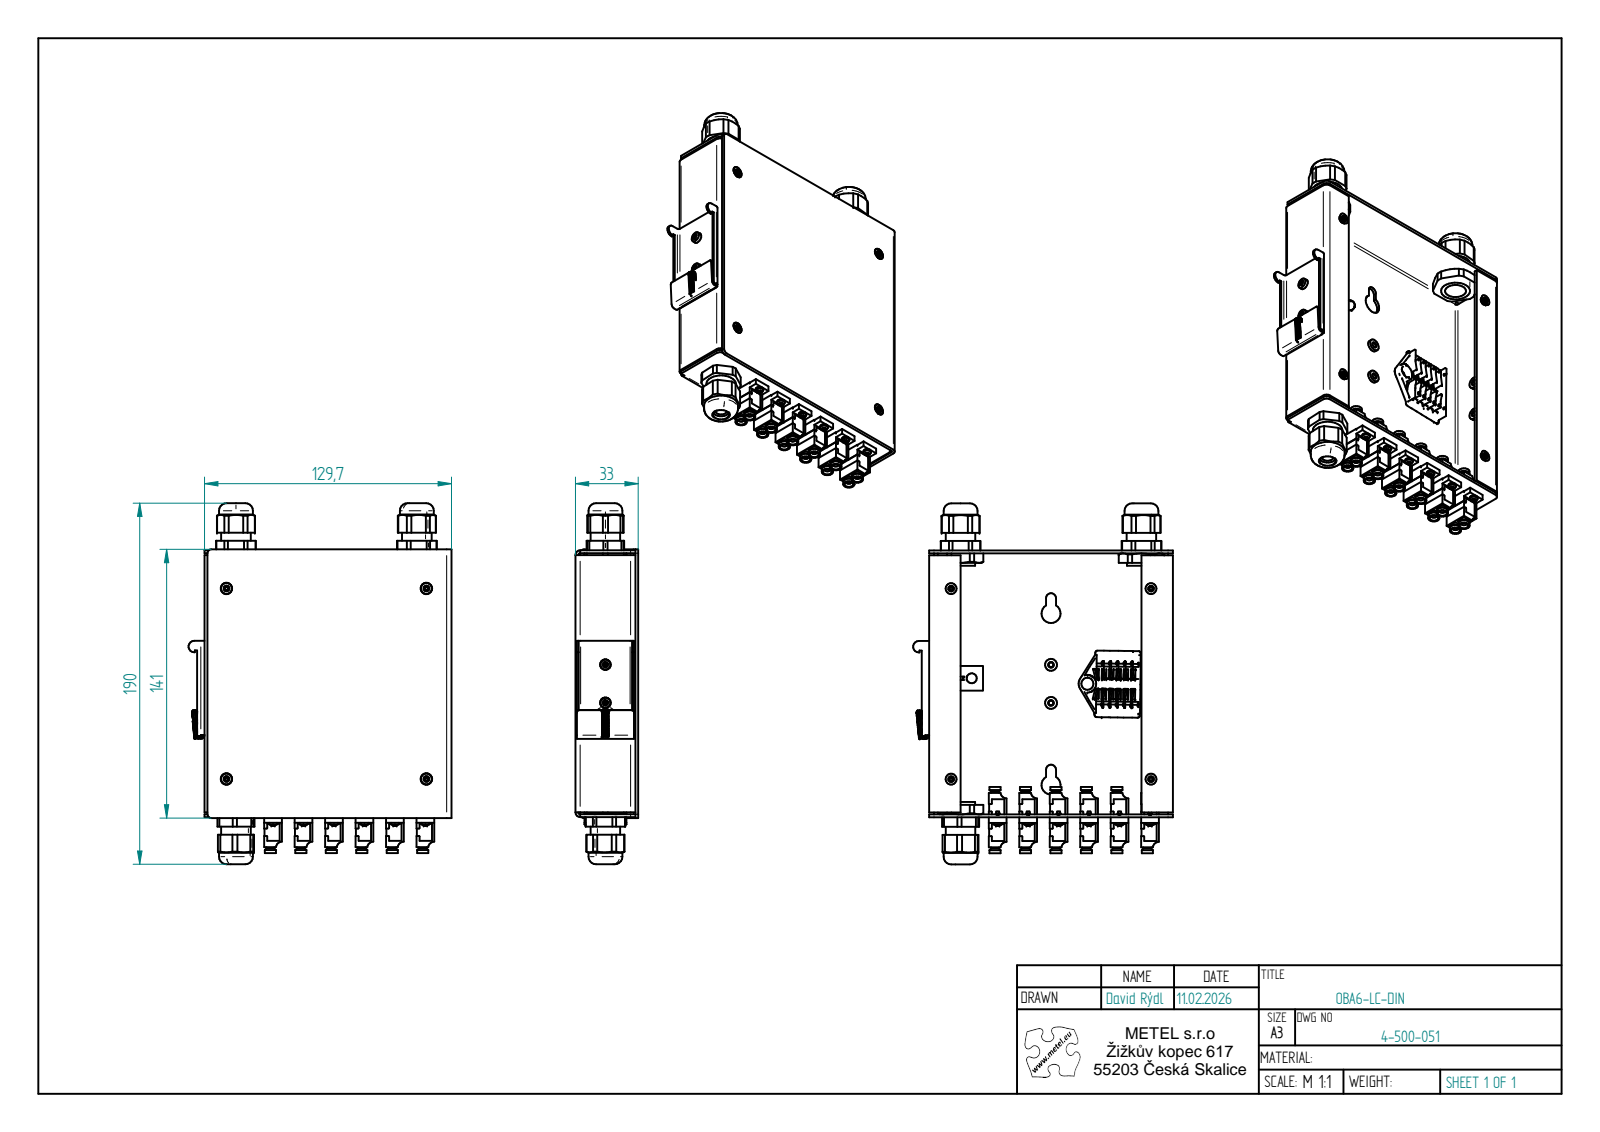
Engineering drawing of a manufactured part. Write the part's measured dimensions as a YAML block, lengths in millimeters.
part_name: "OBA6-LC-DIN; OBA6-DIN_Spodni dil_sestava 2; OBA6-DIN_Spodni dil 2; 19751v-s-m3-2_zi (+8 more)"
step_written_by: "Solid Edge (AUTOMOTIVE_DESIGN)"
units: millimeters
bodies: {solids: 68, faces: 57264, planar: 55759, cylindrical: 847, other: 658}
overall_size: [189.55, 138.11, 33]
volume: 122221
surface_area: 179238
round_holes:
  - {diameter: 3, count: 16}
  - {diameter: 1.8, count: 12}
  - {diameter: 2.03, count: 12}
  - {diameter: 2.49, count: 12}
  - {diameter: 2.5, count: 12}
  - {diameter: 2.46, count: 8}
  - {diameter: 4, count: 4}
  - {diameter: 3.5, count: 2}
  - {diameter: 6, count: 2}
  - {diameter: 8.5, count: 2}
  - {diameter: 9, count: 2}
  - {diameter: 10, count: 2}
round_bosses_or_shafts:
  - {diameter: 5.85, count: 12}
  - {diameter: 4.2, count: 12}
  - {diameter: 4, count: 12}
  - {diameter: 2.74, count: 12}
  - {diameter: 1.5, count: 12}
  - {diameter: 6.3, count: 8}
  - {diameter: 4.22, count: 8}
  - {diameter: 3.8, count: 8}
partial_cylinders:
  - {radius: 0.1, count: 32}
  - {radius: 0.25, count: 24}
  - {radius: 1, count: 15}
  - {radius: 3.17, count: 12}
  - {radius: 2, count: 9}
  - {radius: 2.5, count: 7}
  - {radius: 2.6, count: 2}
  - {radius: 3, count: 2}
face_to_face_distances: [1.5, 31.5, 30, 33, 128.2, 1.7, 126.5, 138.5, 3, 129.7]
hole_center_spacings: [16, 32, 6.02, 12.23, 48, 15.71, 17.2, 18.38]
